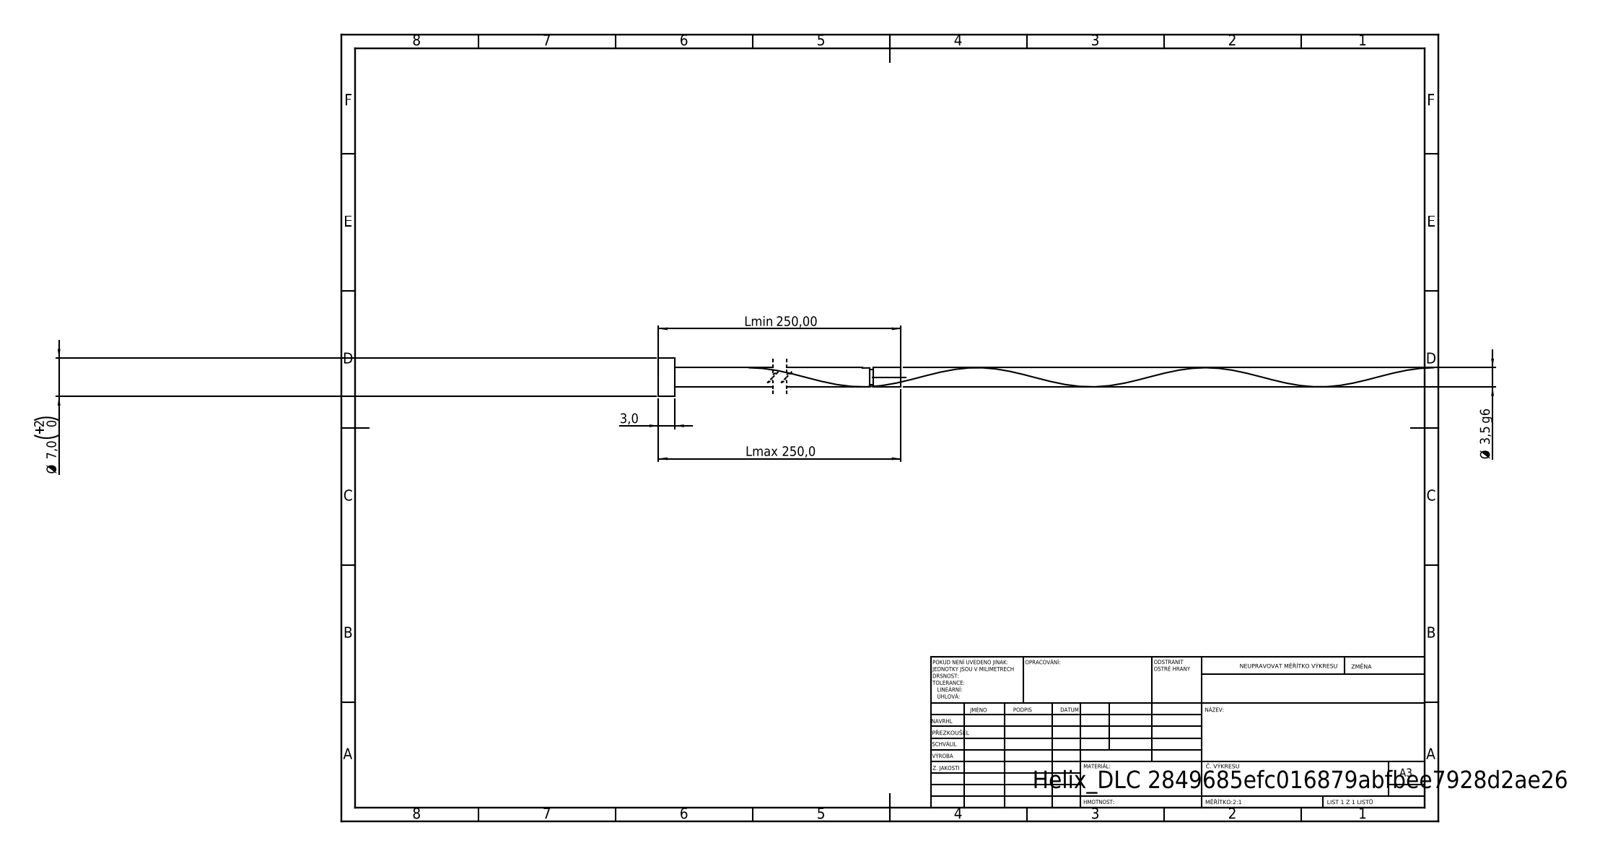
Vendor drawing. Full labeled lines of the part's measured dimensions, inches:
STEP written by: SolidWorks 2019 (CONFIG_CONTROL_DESIGN)
Units: inches
Bodies: 1 solid, 16 faces (6 planar, 9 cylindrical, 1 other)
Overall size (bounding box): 9.843 × 0.276 × 0.276
Volume: 0.183 in³ · Surface area: 5.927 in²
Round bosses / shafts (diameter × count): ⌀0.276 ×1, ⌀0.138 ×1, ⌀0.11 ×1
Main face-to-face distances: 0.118, 9.843, 9.724, 9.646, 9.528, 0.196, 9.619, 9.5, 0.028, 0.224
